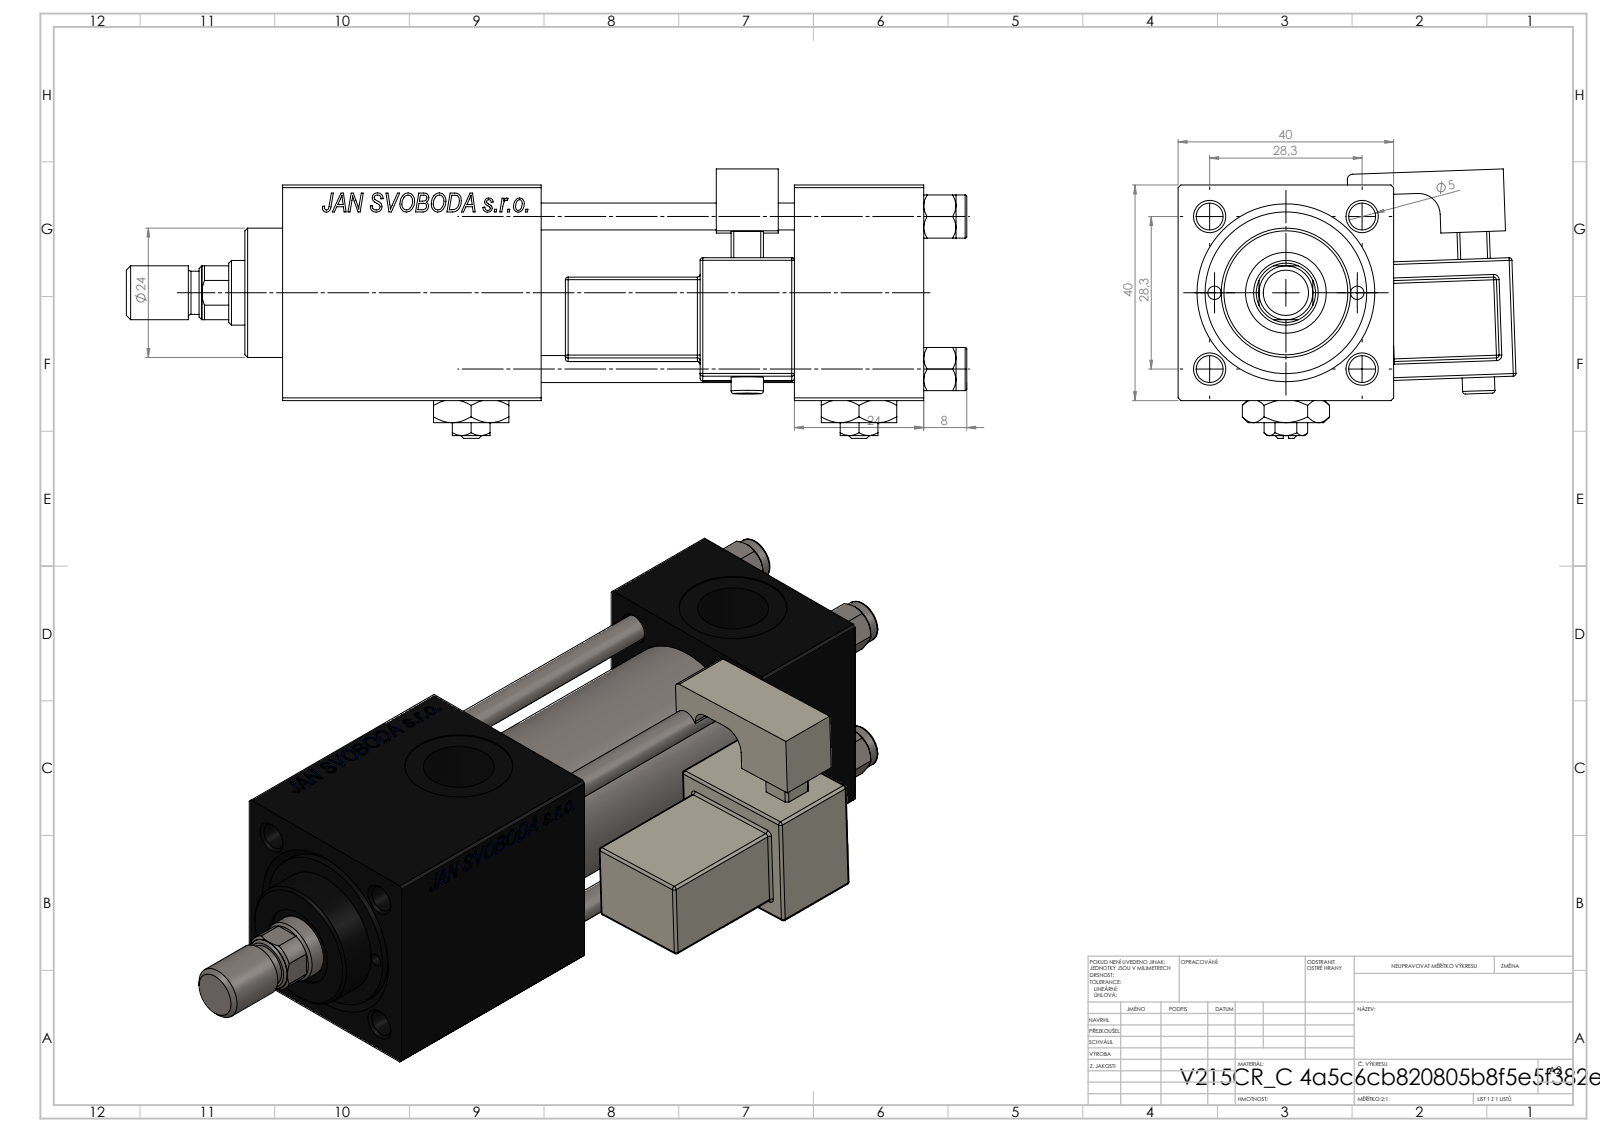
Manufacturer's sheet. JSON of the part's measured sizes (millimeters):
{"part_name": "Zatka_pro_OIL_PORT; V215_VC_A; V215CR_MSU; V215CR_C_Body (+4 more)", "step_written_by": "SolidWorks 2019 (CONFIG_CONTROL_DESIGN)", "units": "millimeters", "bodies": {"solids": 15, "faces": 1347, "planar": 609, "cylindrical": 136, "other": 602}, "overall_size": [156, 62.7, 49.99], "volume_mm3": 161848, "surface_area_mm2": 62942, "round_holes": [[5, 4], [20, 3], [2.5, 2], [7, 2], [13.16, 2], [6.5, 1], [12, 1], [15, 1], [25, 1], [30, 1]], "round_bosses_or_shafts": [[8, 5], [31, 1], [24, 1], [10, 1], [6, 1]], "partial_cylinders_radius": [[0.5, 24], [1, 1], [2.5, 1], [4, 1], [5.5, 1]], "face_to_face_distances": [40, 24, 20, 39.8, 48, 90.3, 66.3, 47, 71, 19.3], "hole_center_spacings": [14.18, 20.01, 28.3, 30.84, 13.25, 40.02, 26.5, 72]}
